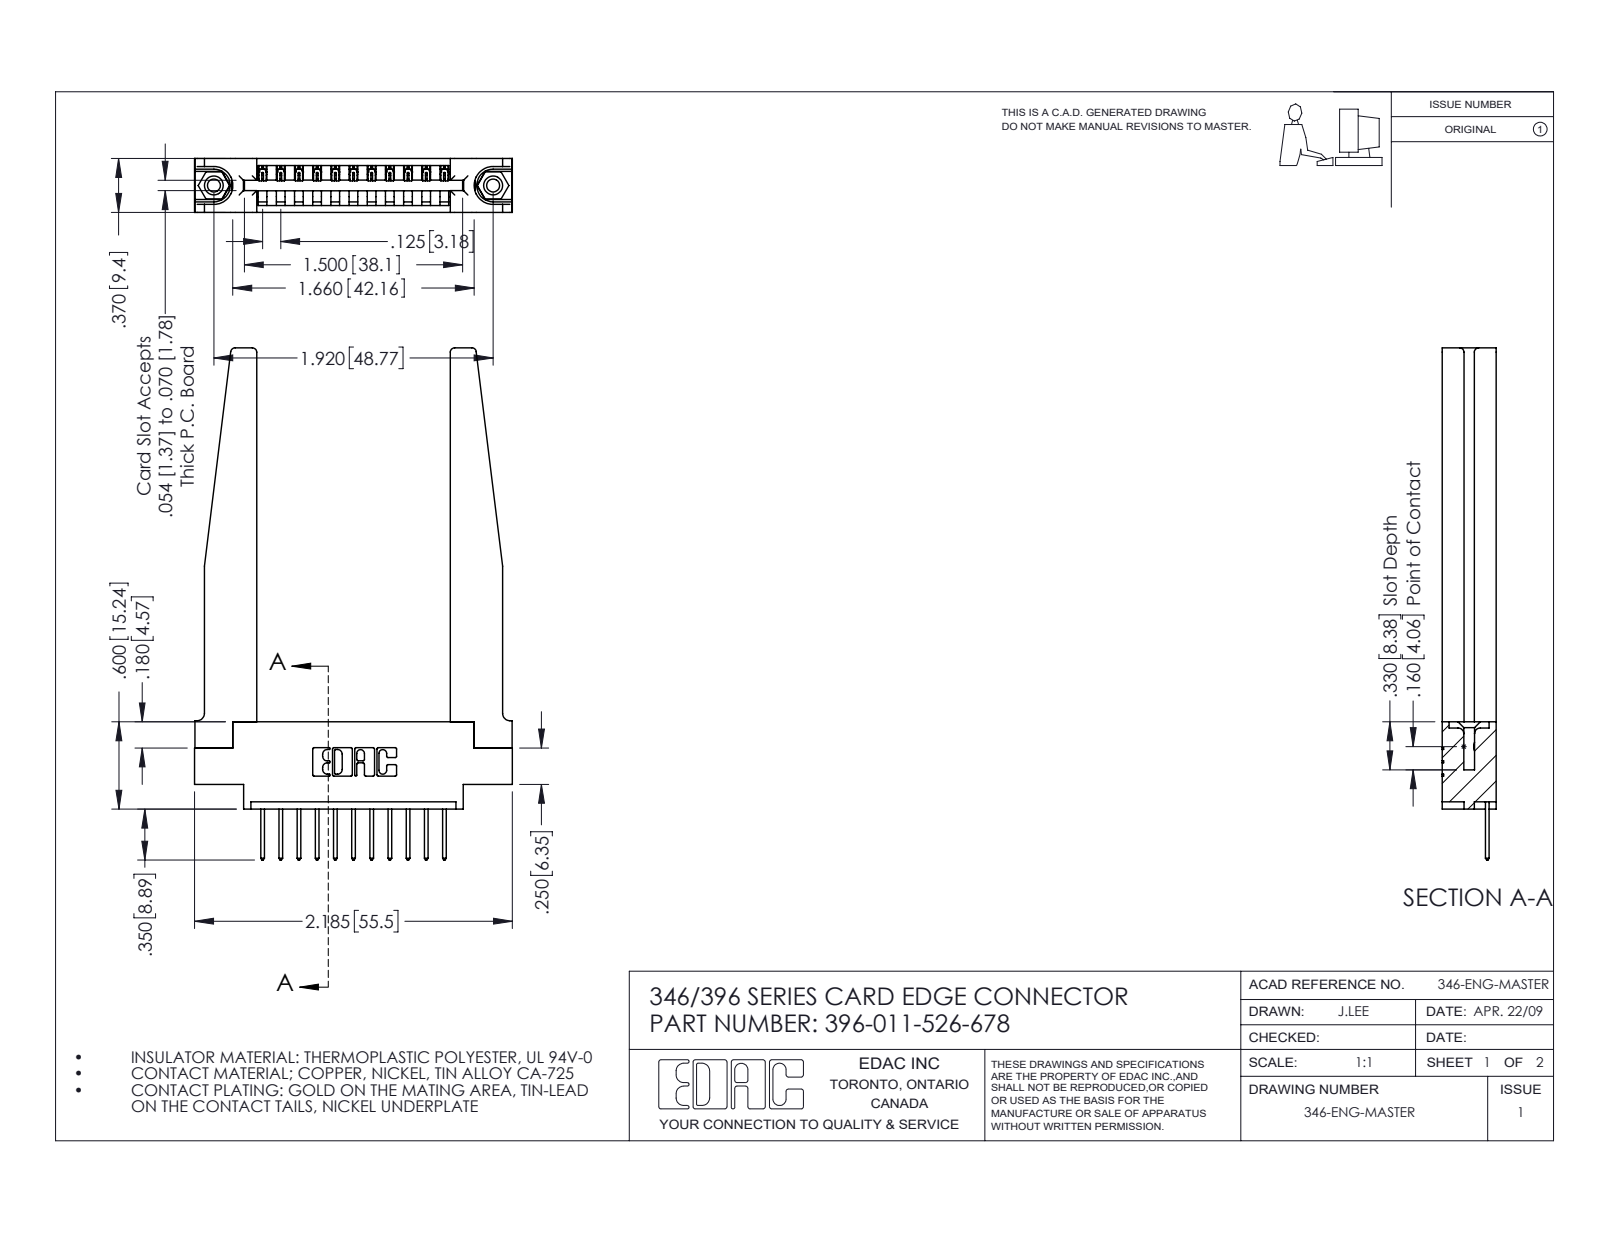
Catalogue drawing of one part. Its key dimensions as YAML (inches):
part_name: "396-011-526-678; 346 Part_0.170 Offset - 0.156 Dia-TH; 346-220-078_345-220-078; 345-292-001_345-293-126 (+1 more)"
step_written_by: "SolidWorks 2016 (CONFIG_CONTROL_DESIGN)"
units: inches
bodies: {solids: 16, faces: 998, planar: 662, cylindrical: 284, other: 52}
overall_size: [3.52, 2.185, 0.37]
volume: 0.723
surface_area: 19.41
round_holes:
  - {diameter: 0.089, count: 2}
  - {diameter: 0.125, count: 2}
  - {diameter: 0.156, count: 2}
  - {diameter: 0.064, count: 1}
round_bosses_or_shafts:
  - {diameter: 0.155, count: 2}
partial_cylinders:
  - {radius: 0.006, count: 22}
  - {radius: 0.01, count: 22}
  - {radius: 0.01, count: 22}
  - {radius: 0.03, count: 8}
  - {radius: 0.007, count: 6}
  - {radius: 0.031, count: 6}
  - {radius: 0.026, count: 3}
  - {radius: 0.031, count: 2}
face_to_face_distances: [0.37, 0.15, 0.072, 0.148, 0.048, 0.322, 0.25, 0.22, 0.102, 0.173]
hole_center_spacings: [0.246, 1.715, 1.92]
